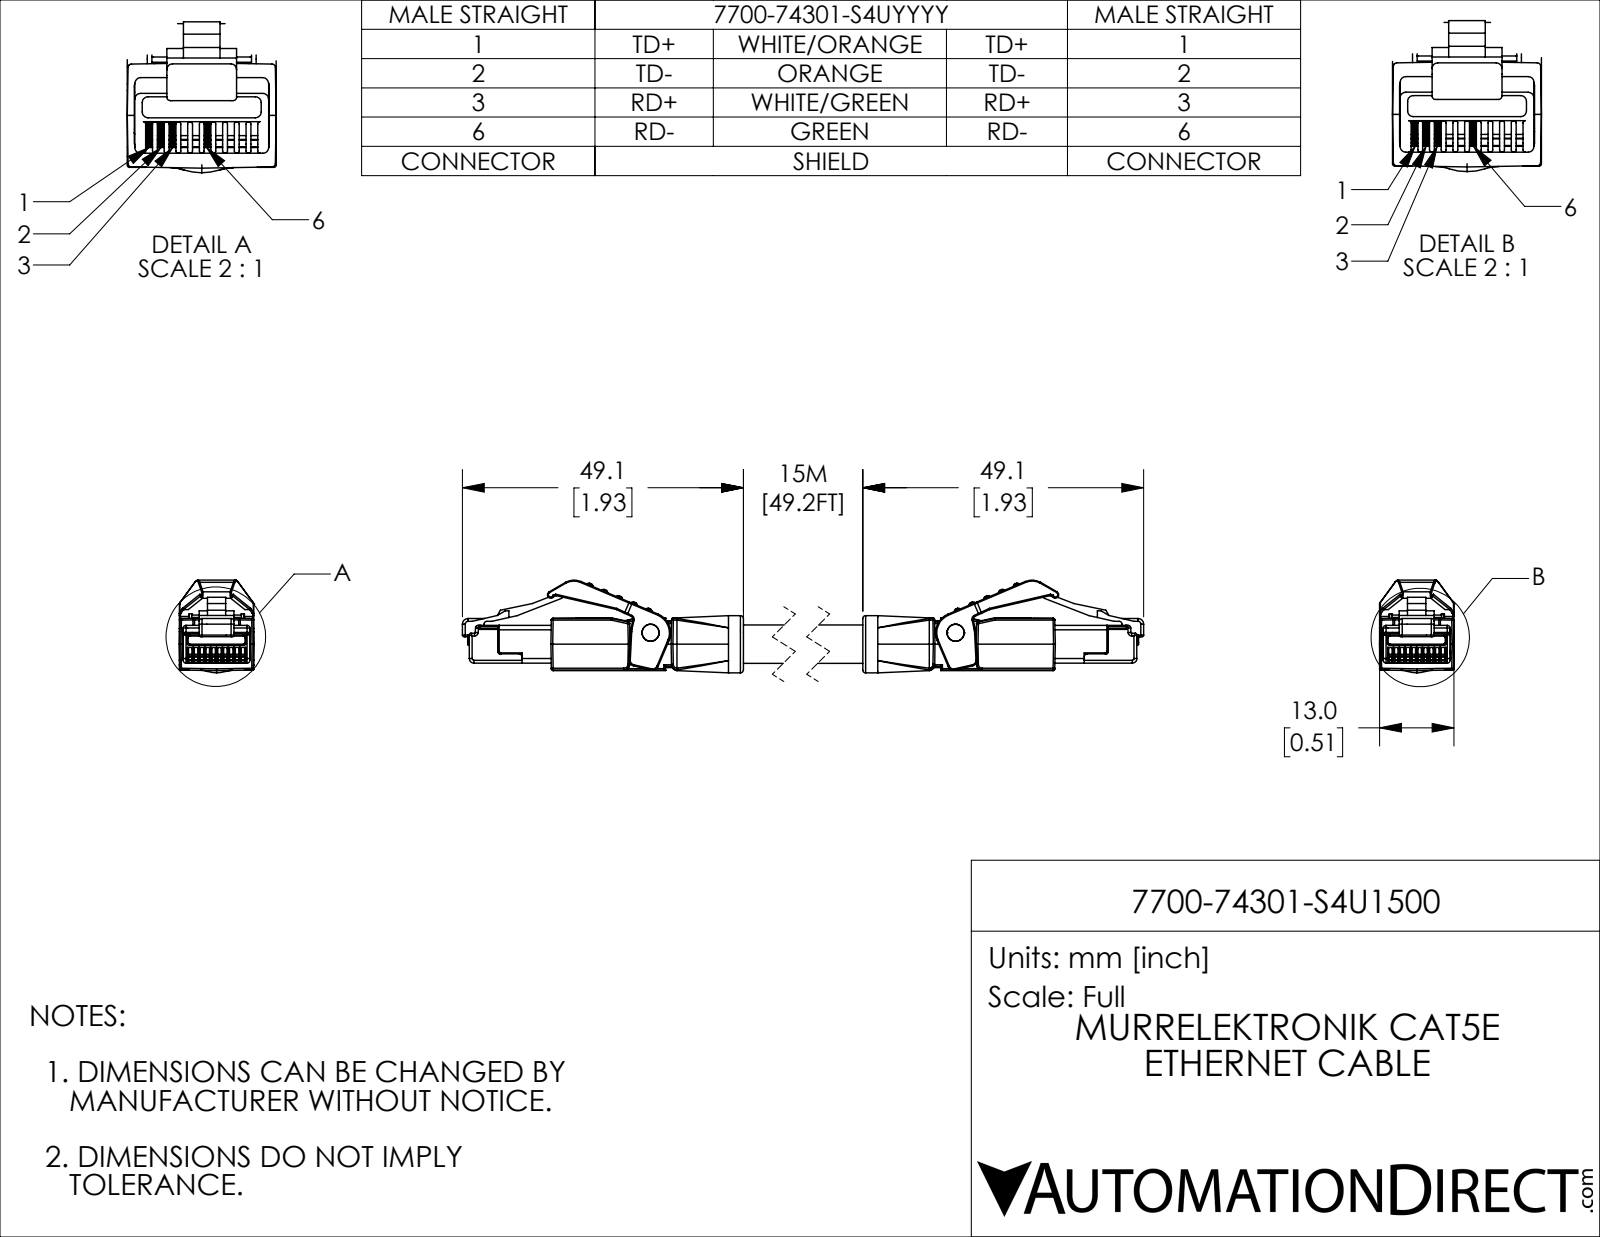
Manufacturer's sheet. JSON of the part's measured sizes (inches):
{"part_name": "7700-74301-S4U1500; 7700-74301-S4U1500_1", "step_written_by": "SolidWorks 2021 (CONFIG_CONTROL_DESIGN)", "units": "inches", "bodies": {"solids": 2, "faces": 1406, "planar": 568, "cylindrical": 566, "other": 272}, "overall_size": [5.112, 0.638, 0.512], "volume_in3": 0.668, "surface_area_in2": 10.82, "round_holes": [[0.118, 2]], "round_bosses_or_shafts": [[0.117, 2], [0.394, 1], [0.264, 1]], "partial_cylinders_radius": [[0.008, 136], [0.012, 114], [0.004, 40], [0.02, 36], [0.039, 10], [0.031, 6], [0.079, 4], [0.197, 4]], "face_to_face_distances": [0.512, 0.362, 0.024, 0.488, 0.026, 0.26, 0.069, 0.443, 0.045, 0.419], "hole_center_spacings": [2.526]}
